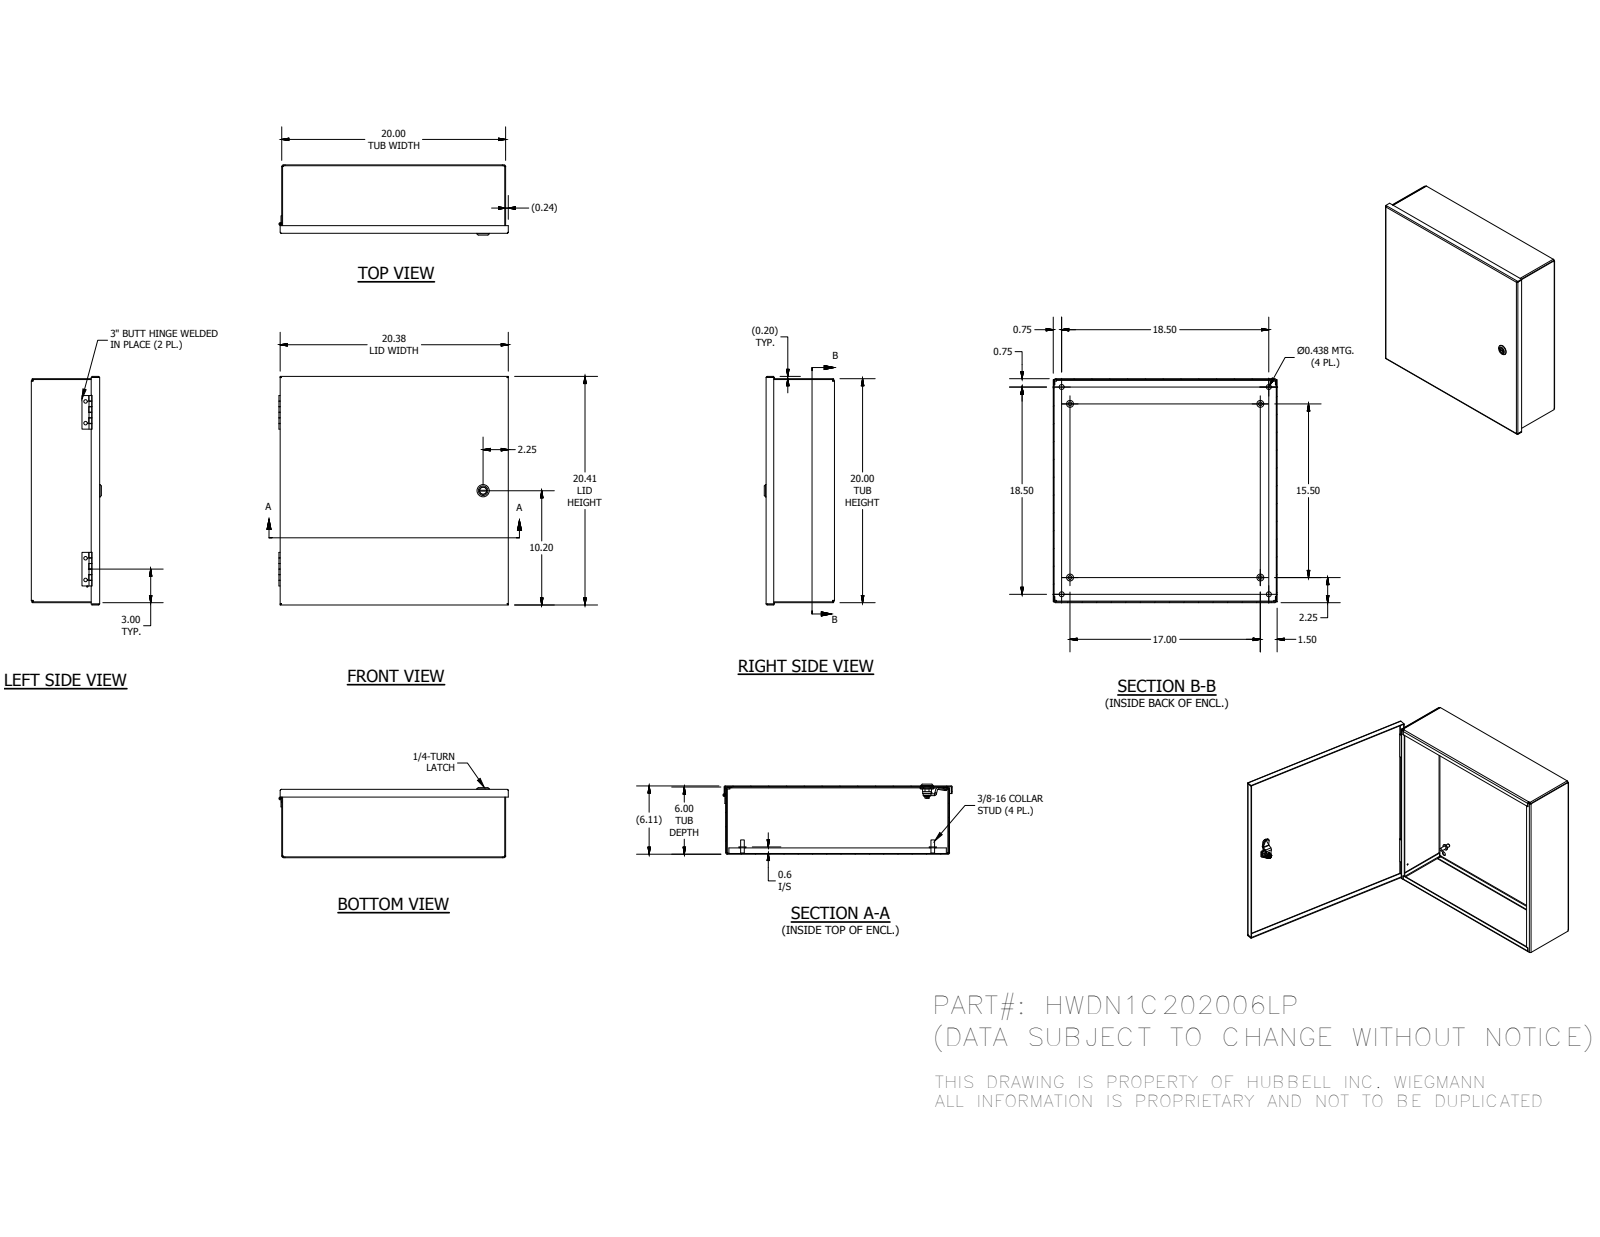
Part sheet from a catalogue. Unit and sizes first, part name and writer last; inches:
Units: inches
Overall size (bounding box): 20.489 × 20.406 × 7.013
Round holes (diameter × count): ⌀0.313 ×4, ⌀0.437 ×4, ⌀0.12 ×1, ⌀0.13 ×1, ⌀0.197 ×1, ⌀0.315 ×1, ⌀0.394 ×1, ⌀0.402 ×1, ⌀0.634 ×1, ⌀0.802 ×1
Round bosses / shafts (diameter × count): ⌀0.625 ×4, ⌀0.33 ×4, ⌀1.102 ×1, ⌀1.063 ×1, ⌀0.906 ×1, ⌀0.78 ×1, ⌀0.622 ×1, ⌀0.598 ×1
Partial cylindrical surfaces — rounded edges, fillets, slot ends (radius × count): R0.012 ×30, R0.063 ×12, R0.137 ×12, R0.02 ×10, R0.031 ×4, R0.105 ×4, R0.157 ×4, R0.016 ×3
Main face-to-face distances: 0.074, 6.781, 19.926, 6.707, 6.855, 19.852, 20, 6.676, 0.105, 0.203
Hole centre spacings: 18.5, 1.94, 9.335, 14, 19.563, 26.163, 0.611, 2.535
Volume: 109.4 in³ · Surface area: 2 976 in²
Bodies: 21 solids, 717 faces (437 planar, 212 cylindrical, 68 other)
Part name (STEP PRODUCT): N1C202006LPBLR; N1C2006LPTB; N1C2020LPLID; 1000-101-GPF_GPD (+8 more)
STEP written by: Autodesk Inventor 2016 (AUTOMOTIVE_DESIGN)
